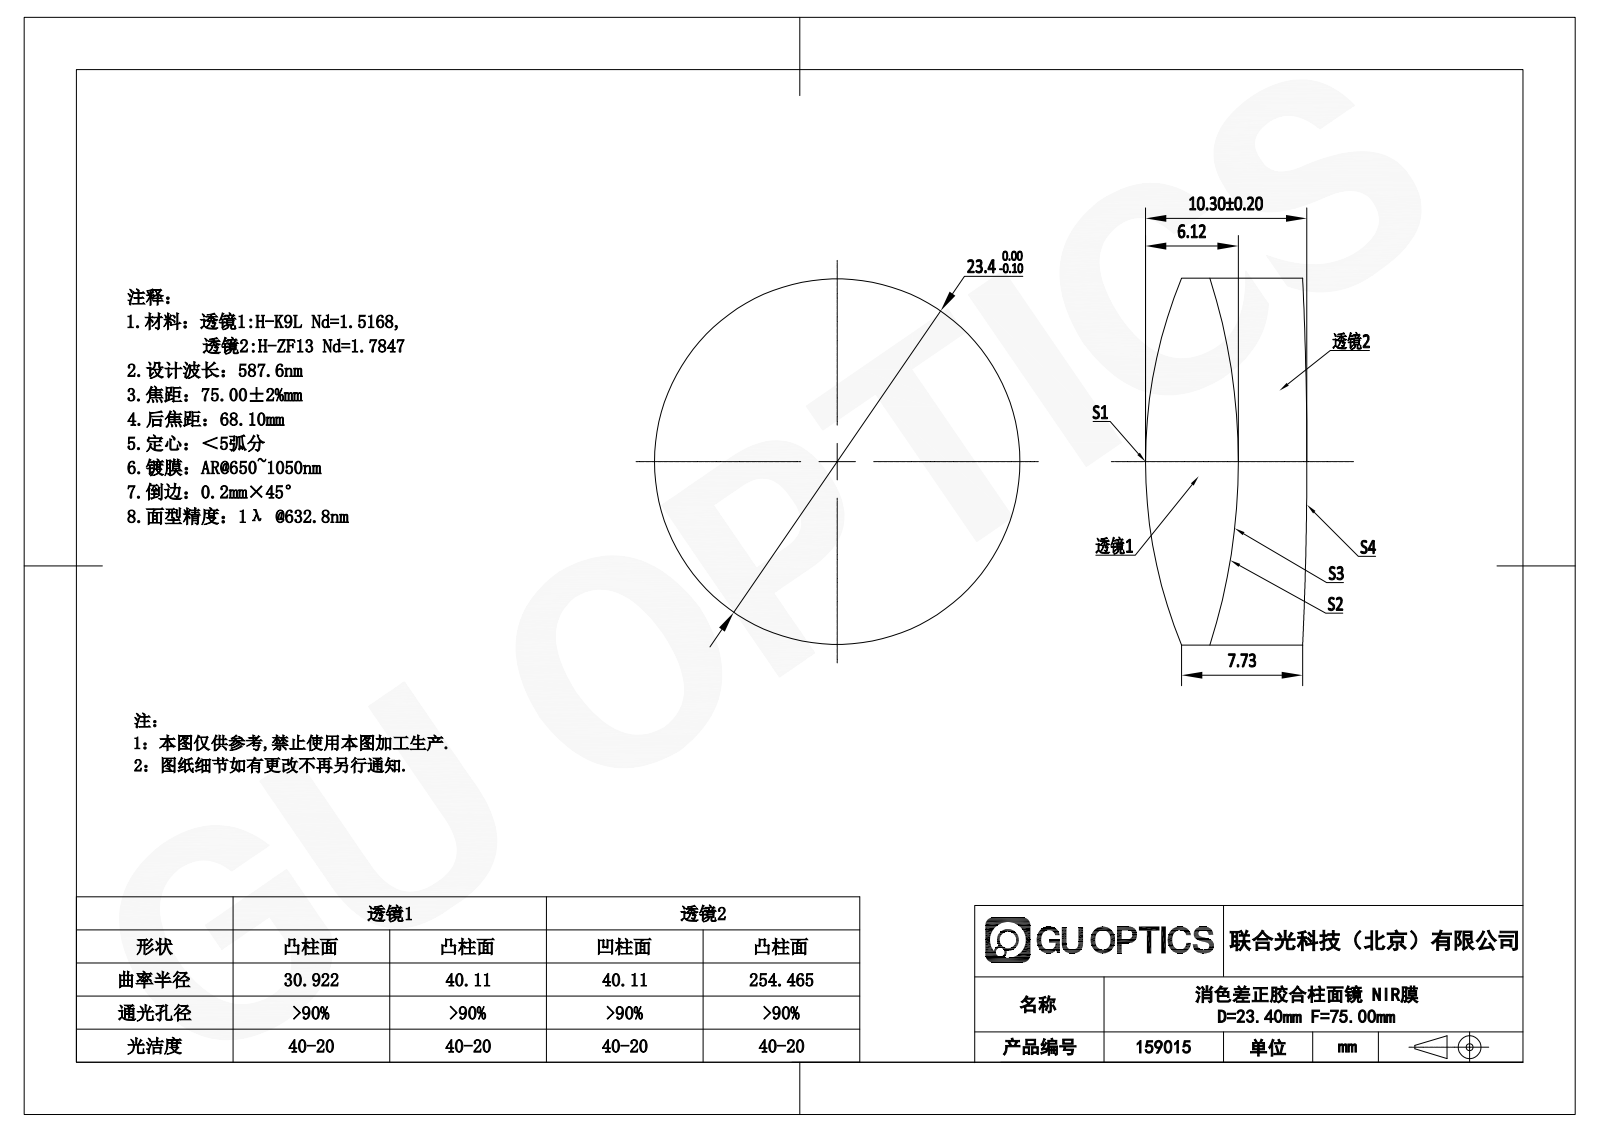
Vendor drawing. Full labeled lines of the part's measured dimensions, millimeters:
Part name (STEP PRODUCT): 159015
STEP written by: SolidWorks 2020 (CONFIG_CONTROL_DESIGN)
Units: millimetres
Bodies: 1 solid, 5 faces (0 planar, 5 cylindrical, 0 other)
Overall size (bounding box): 23.4 × 23.4 × 10.3
Volume: 4 158 mm³ · Surface area: 1 532 mm²
Round bosses / shafts (diameter × count): ⌀23.4 ×1
Partial cylindrical surfaces — rounded edges, fillets, slot ends (radius × count): R30.92 ×1, R254.47 ×1
